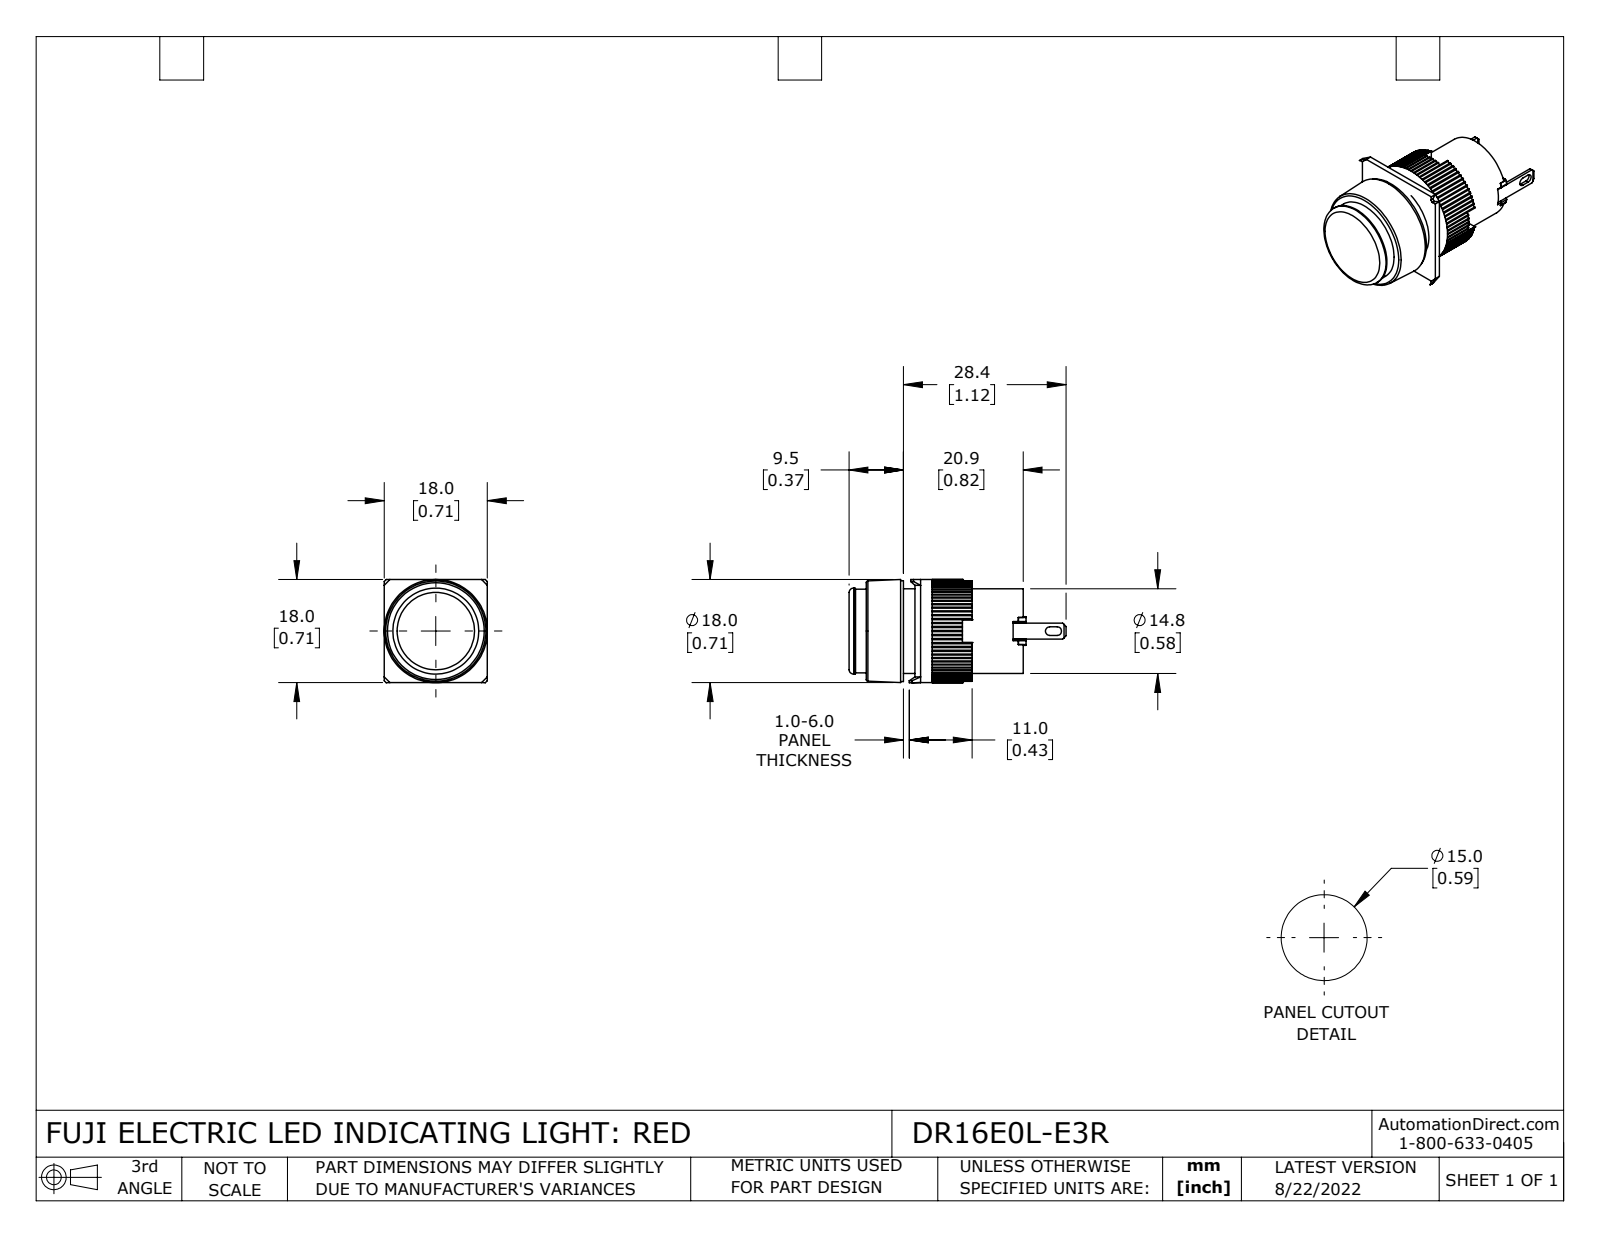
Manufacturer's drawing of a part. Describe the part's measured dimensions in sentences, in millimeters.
The part is named "DR16E0L-E3R". Its 3-D file was written by "SolidWorks 2021 (CONFIG_CONTROL_DESIGN)". It is 10 solids with 476 faces: 295 planar, 171 cylindrical and 10 other. Overall it measures 37.9 by 18 by 18 millimeters. Its volume is 5 720 cubic millimeters and its surface area 4 661 square millimeters. Round holes: 1 of diameter 13.8, 1 of diameter 14.6, 1 of diameter 14.8. Round bosses or shafts: 1 of diameter 18, 1 of diameter 17.6, 1 of diameter 15. Partial cylindrical surfaces (rounded edges, fillets, slot ends): 80 of radius 0.3, 8 of radius 0.2, 2 of radius 0.8. The main face-to-face distances are 3.5, 8.9, 17.9, 9, 12.5, 5.4, 11.5, 21.4, 2.5, 1.
